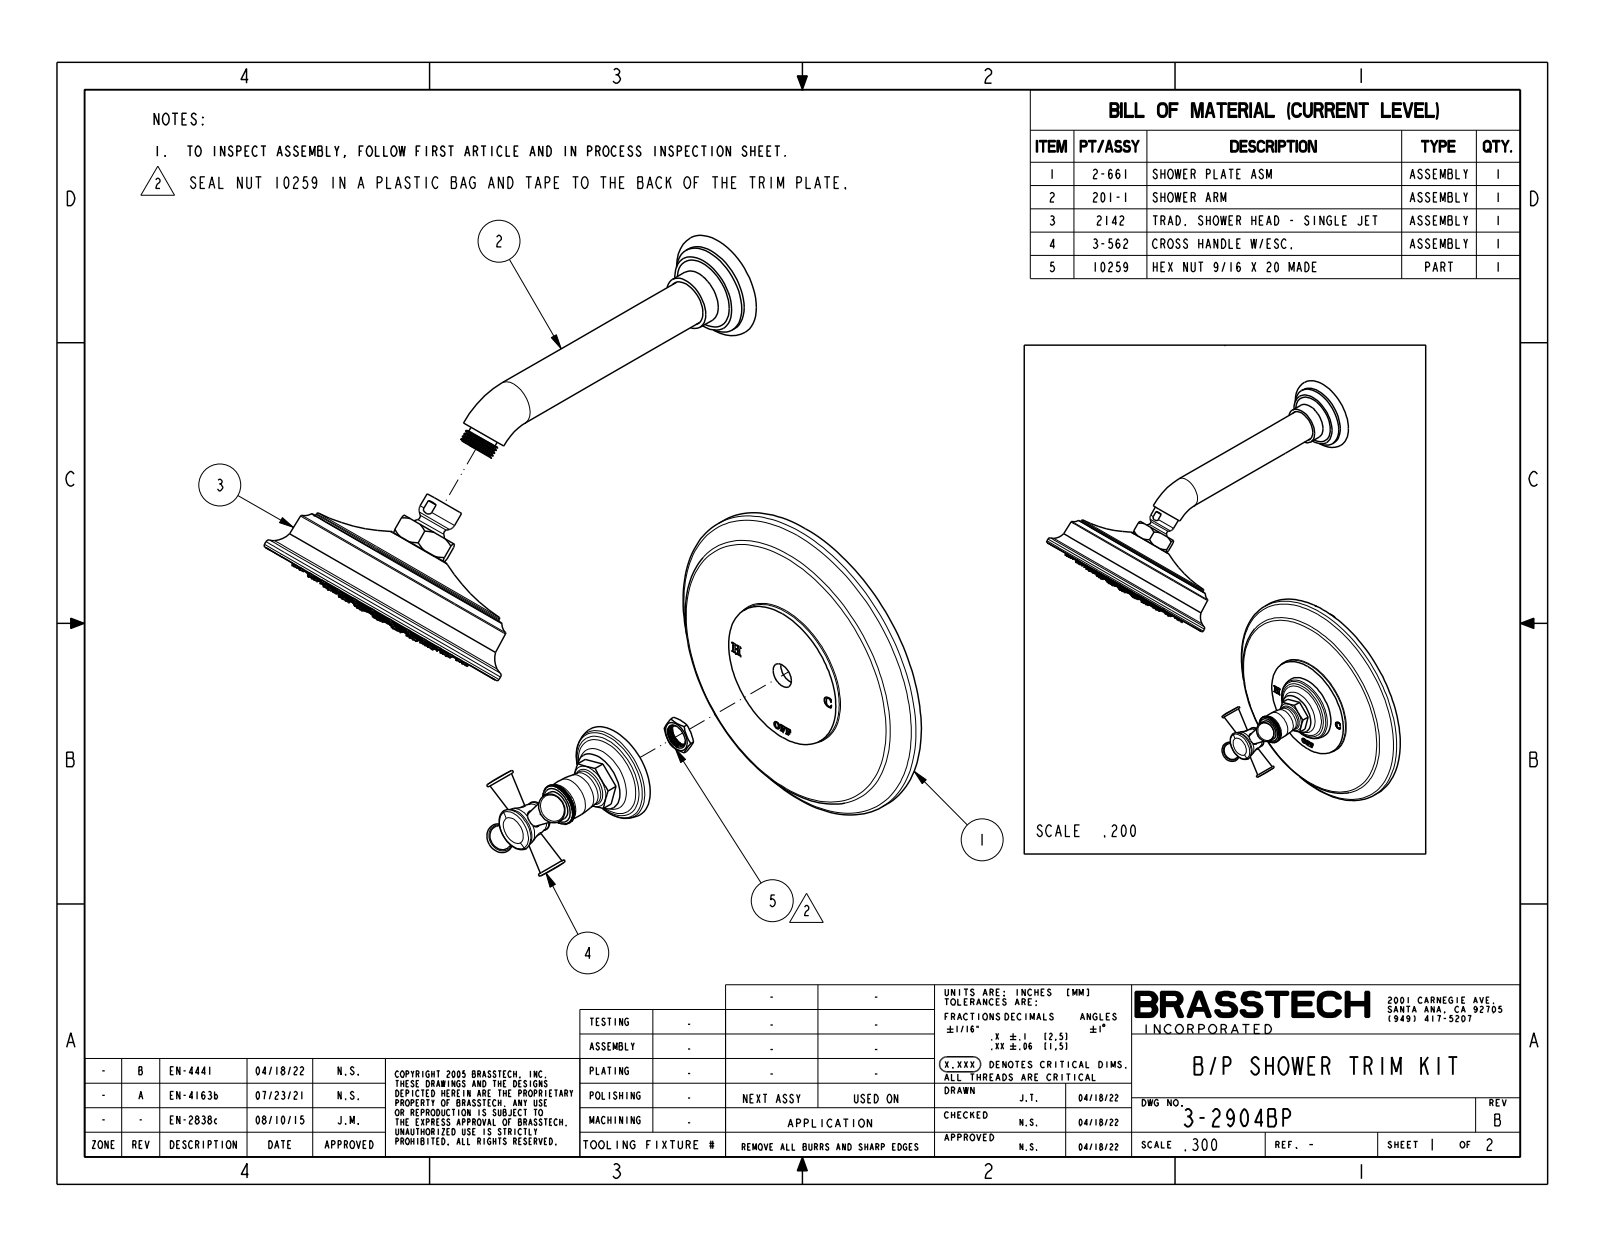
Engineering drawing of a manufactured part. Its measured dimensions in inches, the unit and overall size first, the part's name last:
Units: inches
Overall size (bounding box): 17 × 11.998 × 7.5
Round holes (diameter × count): ⌀0.05 ×90, ⌀0.125 ×90, ⌀0.187 ×1, ⌀0.22 ×1, ⌀0.5 ×1, ⌀0.59 ×1, ⌀0.604 ×1, ⌀5.275 ×1, ⌀7.25 ×1
Round bosses / shafts (diameter × count): ⌀0.198 ×60, ⌀7.5 ×1, ⌀6.2 ×1, ⌀4.83 ×1, ⌀2.11 ×1, ⌀1.42 ×1, ⌀1.263 ×1, ⌀1.1 ×1
Main face-to-face distances: 0.125, 0.25, 0.125, 0.485, 0.015, 0.735, 0.61, 0.5, 0.625, 0.75
Hole centre spacings: 1.84, 0.48, 1.84, 0.952, 2.27, 0.474, 1.408, 2.24
Volume: 54.15 in³ · Surface area: 276.7 in²
Bodies: 39 solids, 1981 faces (656 planar, 522 cylindrical, 803 other)
Part name (STEP PRODUCT): 3-2904BP
STEP written by: CREO PARAMETRIC BY PTC INC, 2018400 (AUTOMOTIVE_DESIGN)
